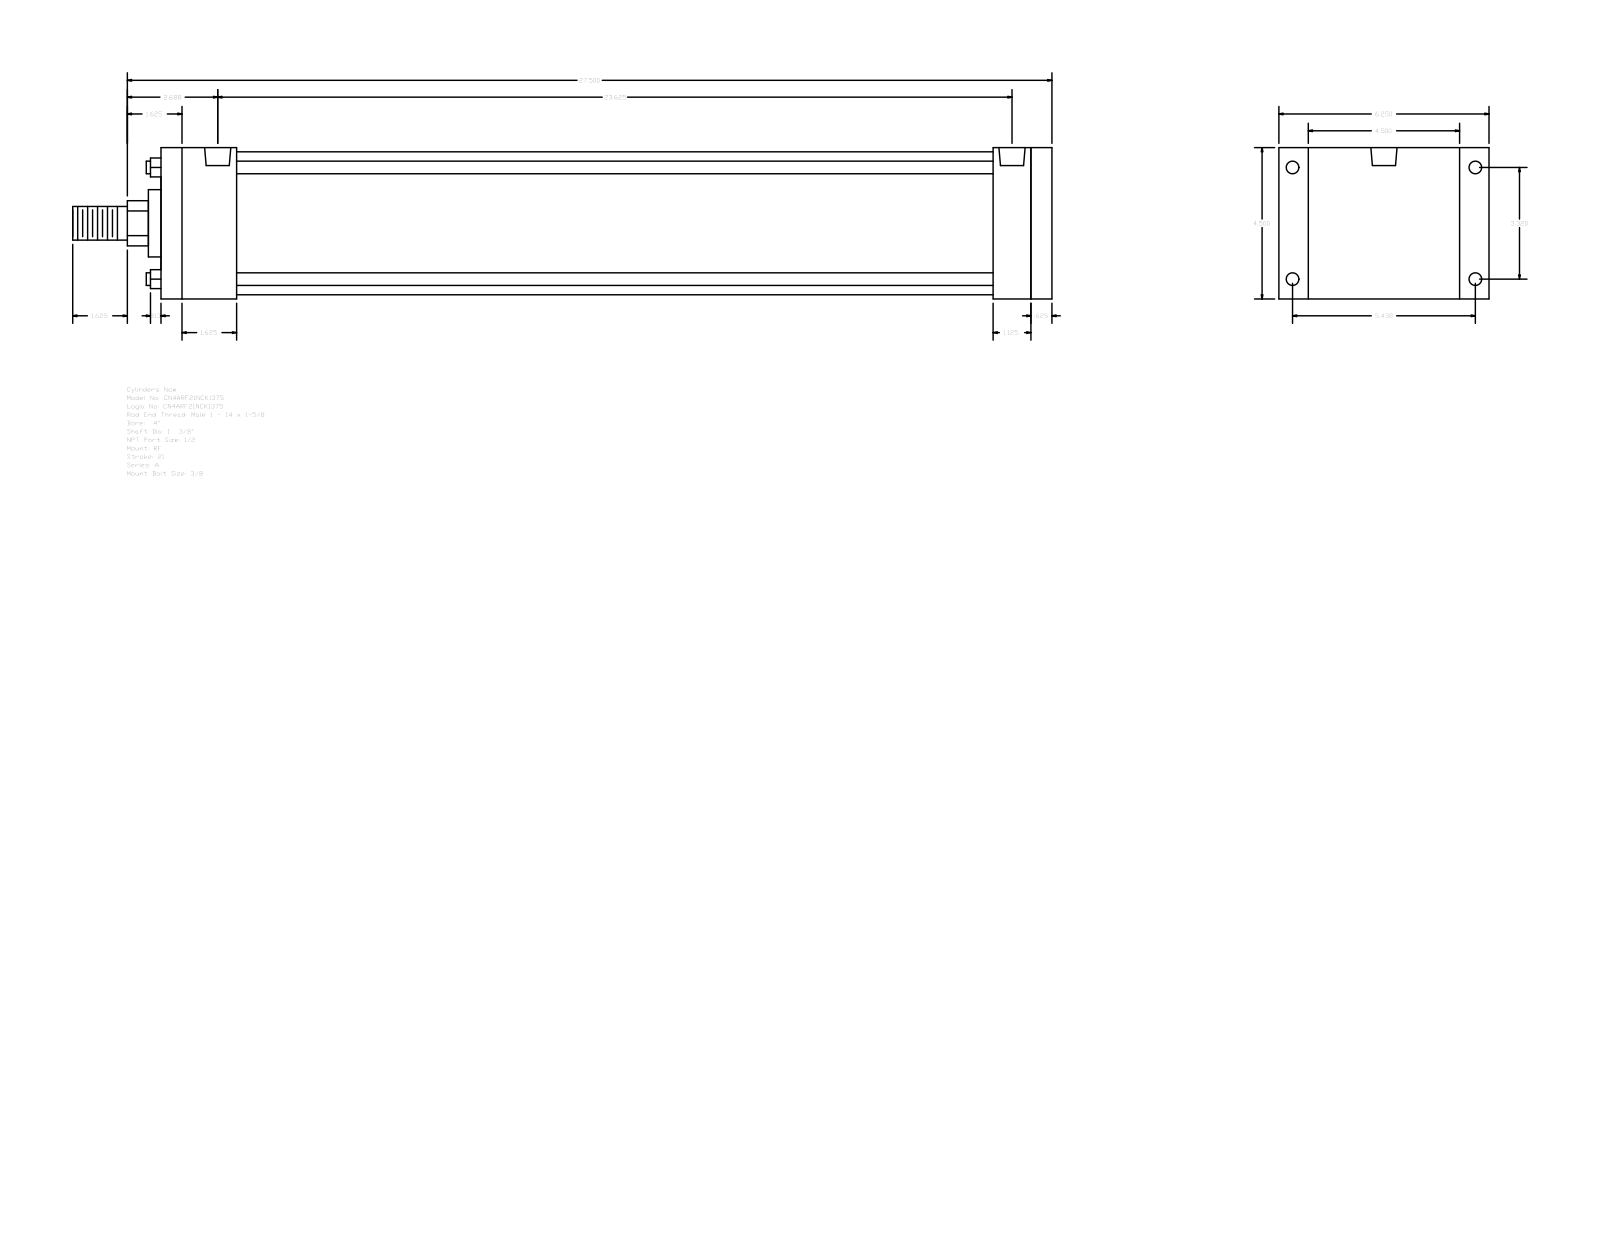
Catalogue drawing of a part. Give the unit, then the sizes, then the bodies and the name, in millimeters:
Units: millimetres
Overall size (bounding box): 739.77 × 158.75 × 114.3
Round holes (diameter × count): ⌀8.73 ×4, ⌀9.53 ×4, ⌀19.77 ×2
Round bosses / shafts (diameter × count): ⌀9.53 ×4, ⌀107.95 ×1, ⌀50.8 ×1, ⌀34.92 ×1, ⌀25.4 ×1
Partial cylindrical surfaces — rounded edges, fillets, slot ends (radius × count): R17.06 ×1
Main face-to-face distances: 114.3, 673.1, 15.88, 657.22, 57.15, 22.23, 136.53, 628.65, 28.57, 44.45
Hole centre spacings: 3.18, 84.32, 138.12, 161.82, 593.72, 596.9, 600.08
Bodies: 0 solids, 92 faces (64 planar, 28 cylindrical, 0 other)
Part name (STEP PRODUCT): A_RF__0400_1.375
STEP written by: GSSL Pune (CONFIG_CONTROL_DESIGN)
